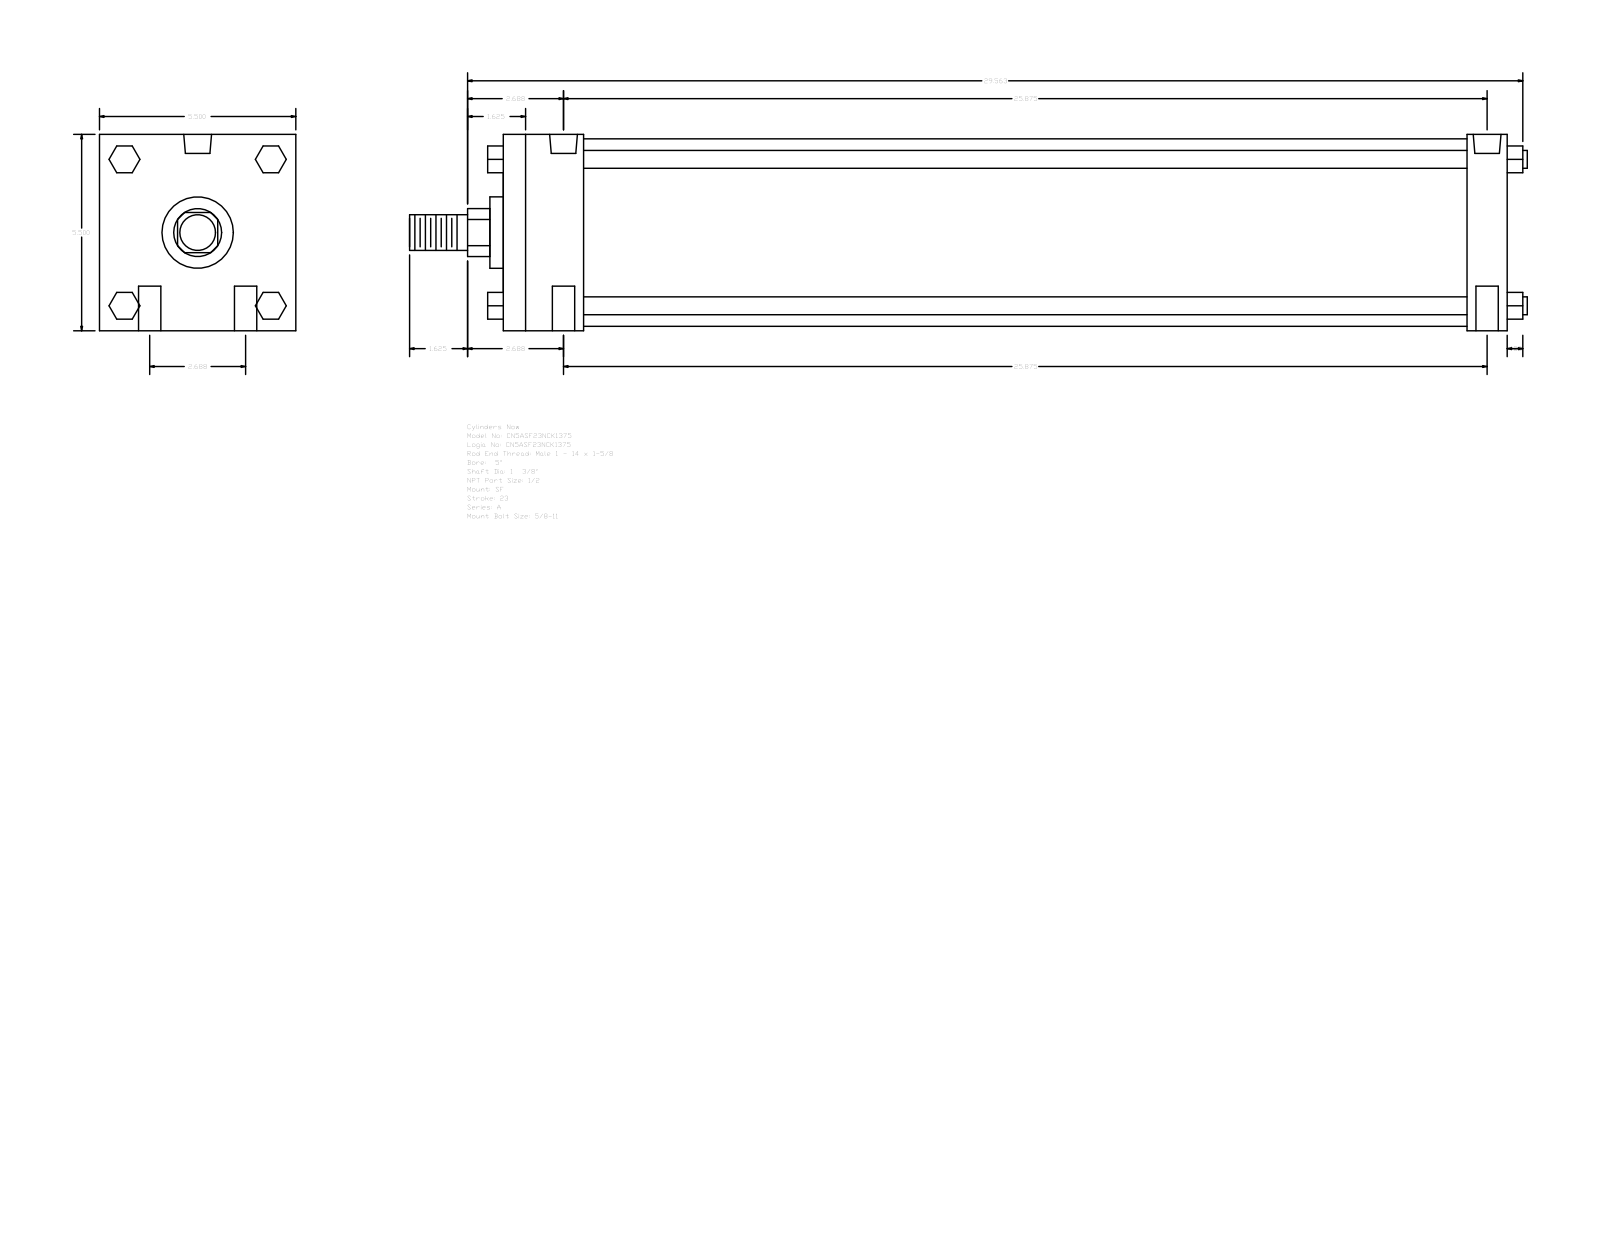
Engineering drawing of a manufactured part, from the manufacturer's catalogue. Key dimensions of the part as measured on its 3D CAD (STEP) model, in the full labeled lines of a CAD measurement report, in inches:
Part name (STEP PRODUCT): A_SF__0500_1.375
STEP written by: GSSL Pune (CONFIG_CONTROL_DESIGN)
Units: inches
Bodies: 0 solids, 124 faces (94 planar, 30 cylindrical, 0 other)
Overall size (bounding box): 31.313 × 5.5 × 5.5
Round holes (diameter × count): ⌀0.625 ×4, ⌀0.344 ×2, ⌀0.778 ×2
Round bosses / shafts (diameter × count): ⌀0.5 ×4, ⌀5.25 ×1, ⌀2 ×1, ⌀1.375 ×1, ⌀1 ×1
Partial cylindrical surfaces — rounded edges, fillets, slot ends (radius × count): R0.672 ×1
Main face-to-face distances: 5.5, 28.125, 2.25, 27, 24.75, 25.875, 1.125, 0.75, 2.05, 3.55
Hole centre spacings: 1.344, 25.91, 25.875, 2.687, 26.015, 25.687
